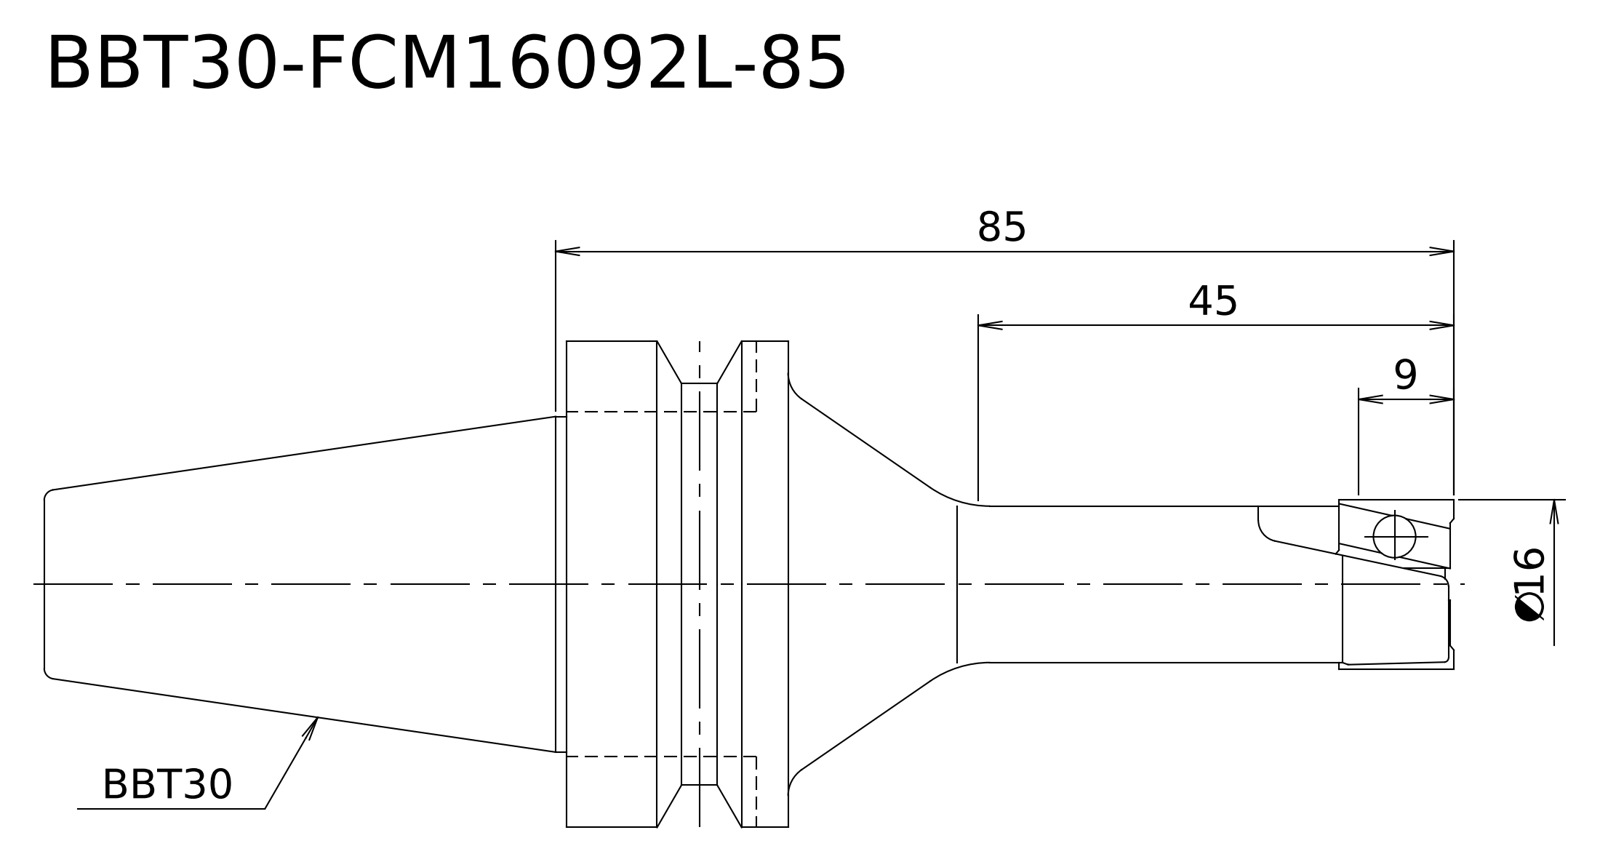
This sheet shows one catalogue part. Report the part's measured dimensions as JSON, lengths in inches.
{"step_written_by": "Kubotek KeyCreator V8.5.1 (14335) (CONFIG_CONTROL_DESIGN)", "units": "inches", "bodies": {"solids": 1, "faces": 17, "planar": 4, "cylindrical": 6, "other": 7}, "overall_size": [5.252, 1.811, 1.811], "volume_in3": 4.514, "surface_area_in2": 20.26, "round_bosses_or_shafts": [[1.811, 1], [1.496, 1], [1.25, 1], [0.63, 1], [0.583, 1]], "face_to_face_distances": [0.827, 2.772, 1.945, 2.48, 3.307, 5.252]}
